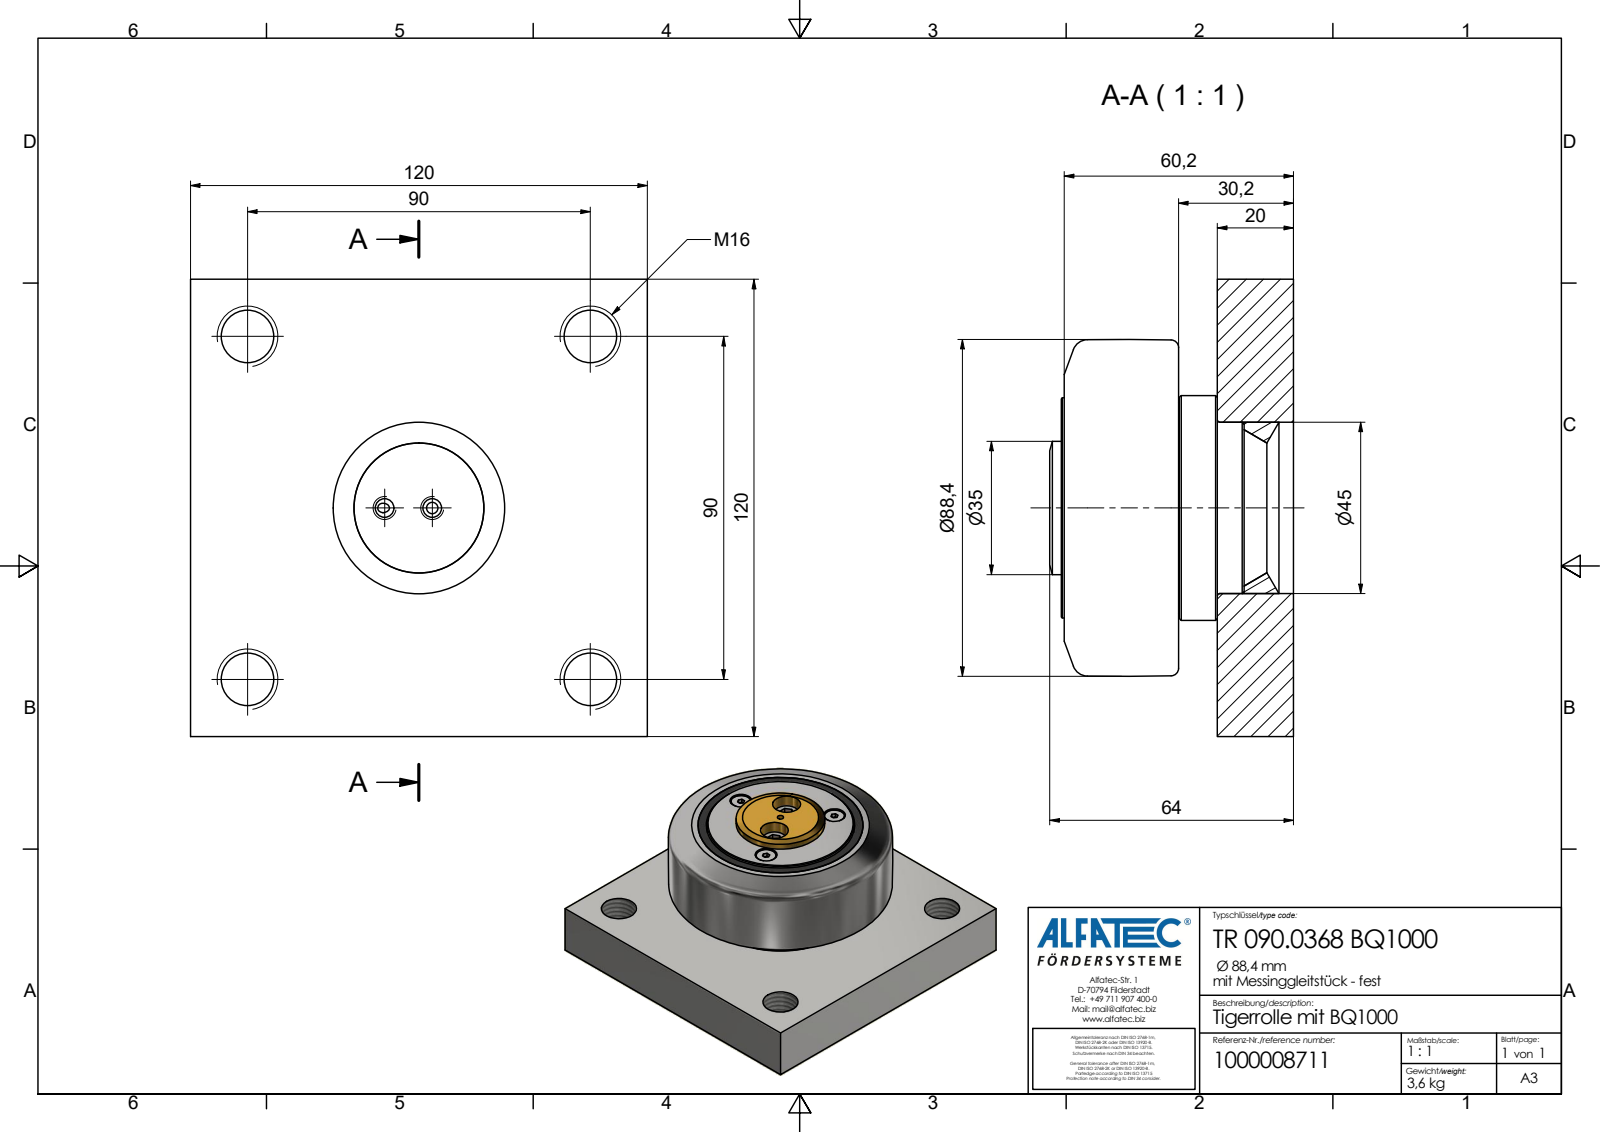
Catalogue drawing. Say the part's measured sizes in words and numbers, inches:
The part is named "TR 090.0368 BQ1000_Kontur". Its 3-D file was written by "Autodesk Inventor 2020 (AP242_MANAGED_MODEL_BASED_3D_ENGINEERING_MIM_LF)". It is 1 solid with 80 faces: 44 planar, 22 cylindrical and 14 other. Overall it measures 4.724 by 4.724 by 2.52 inches. Its volume is 29.07 cubic inches and its surface area 91.79 square inches. Round holes: 4 of diameter 0.545, 3 of diameter 0.339, 2 of diameter 0.098, 2 of diameter 0.194, 2 of diameter 0.433, 1 of diameter 0.118, 1 of diameter 1.772. Round bosses or shafts: 3 of diameter 0.307, 1 of diameter 2.323, 1 of diameter 2.276, 1 of diameter 2.177, 1 of diameter 1.378. The main face-to-face distances are 0.787, 4.724, 1.189, 0.402, 1.181, 2.37, 1.583, 2.402, 1.614, 1.213. The hole center spacings are 2.506, 3.543, 0.866, 1.5, 0.364, 0.754, 0.943, 1.094.
